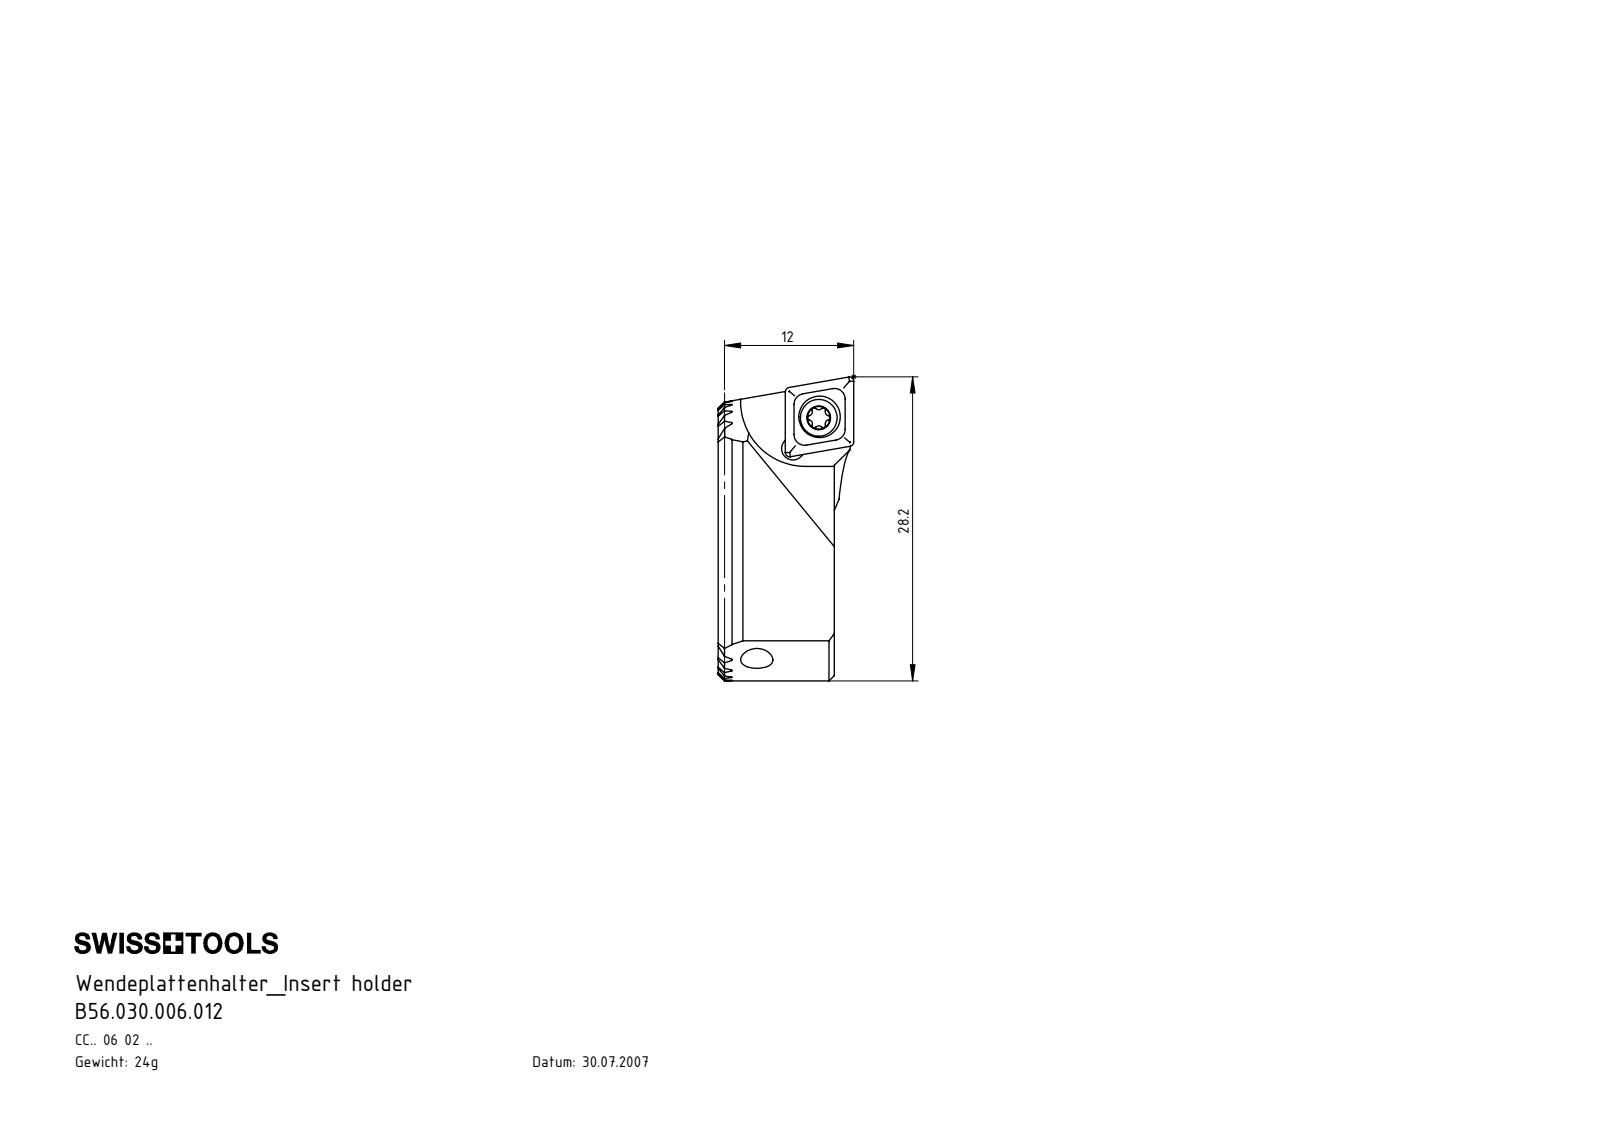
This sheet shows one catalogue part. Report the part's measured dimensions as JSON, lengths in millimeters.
{"part_name": "WCA-ER2.001.006_A; BV1-WCA.K11.012_B_mit beschriftung; CCMT060204; KVT_MB_600_030 (+1 more)", "step_written_by": "SolidWorks 2017 (AUTOMOTIVE_DESIGN)", "units": "millimeters", "bodies": {"solids": 6, "faces": 309, "planar": 172, "cylindrical": 49, "other": 88}, "overall_size": [28.2, 18.6, 12.58], "volume_mm3": 2974, "surface_area_mm2": 2775, "round_holes": [[2, 3], [2.05, 1], [2.1, 1], [2.38, 1], [2.8, 1], [3.85, 1]], "round_bosses_or_shafts": [[3.4, 1], [3, 1], [2.5, 1]], "partial_cylinders_radius": [[0.14, 10], [0.21, 6], [0.36, 4], [0.36, 2], [2.7, 2], [5.75, 2], [6, 1], [13, 1]], "face_to_face_distances": [1.73, 3.46, 8.66, 6.93, 10.39, 5.2, 5.19, 6.92, 5, 12.12], "hole_center_spacings": [3.73, 3.85]}
